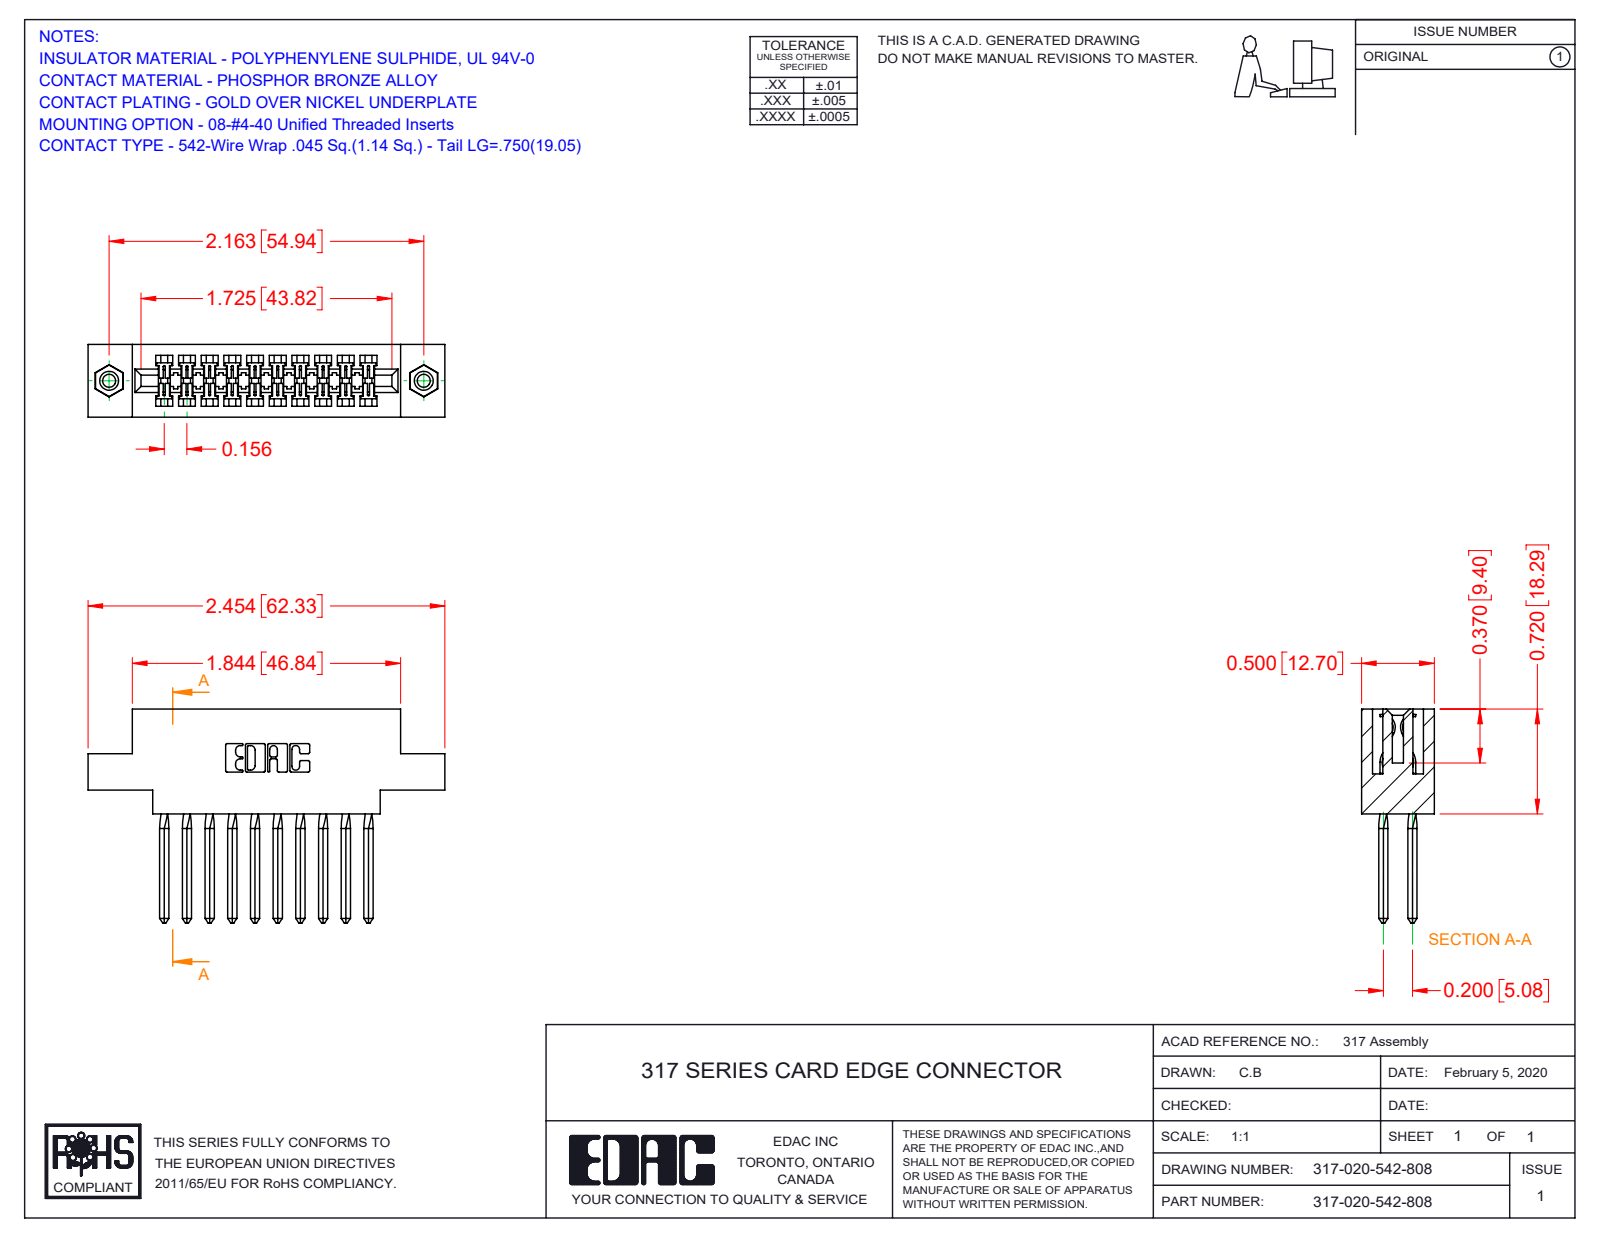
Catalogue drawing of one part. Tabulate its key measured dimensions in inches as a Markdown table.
| quantity | value |
| --- | --- |
| part name | 317-290-003_542; 317-020-542-808; 345-250-001_345-250-003-102; 317 Part_.156 Dia - TI |
| STEP written by | SolidWorks 2016 (CONFIG_CONTROL_DESIGN) |
| units | inches |
| bodies | 23 solids, 1302 faces (1010 planar, 196 cylindrical, 96 other) |
| overall size | 2.454 × 1.47 × 0.5 |
| volume | 0.561 in³ |
| surface area | 18.25 in² |
| round holes (diameter × count) | 0.089 × 2, 0.125 × 2, 0.156 × 2 |
| round bosses / shafts (diameter × count) | 0.155 × 2 |
| partial cylindrical surfaces (radius × count) | 0.006 × 40, 0.01 × 22, 0.007 × 6, 0.031 × 6, 0.026 × 3, 0.074 × 2, 0.089 × 2, 0.1 × 2 |
| main face-to-face distances | 0.5, 0.075, 0.425, 0.11, 0.22, 0.116, 0.35, 0.136, 0.156, 0.2 |
| hole center spacings | 2.163 |
